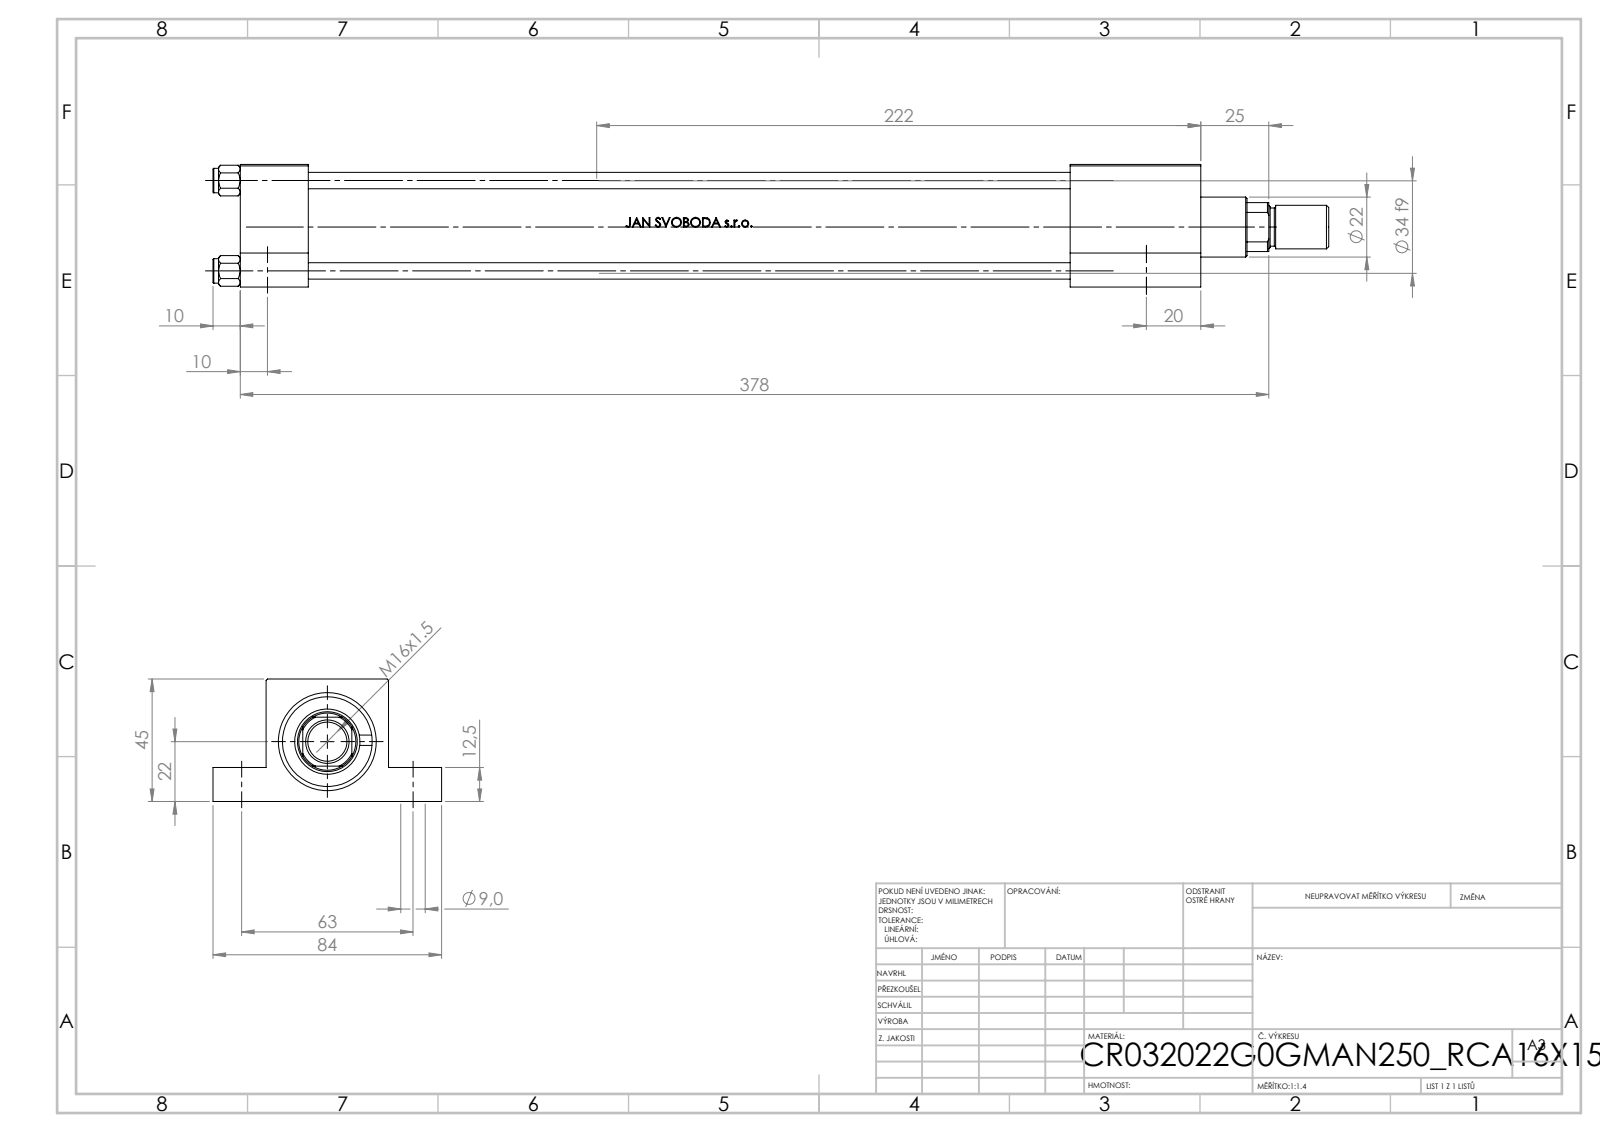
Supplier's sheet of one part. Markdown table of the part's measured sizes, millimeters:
| quantity | value |
| --- | --- |
| part name | V215CR_G_TYCINKA; V215_VC_A; ROD_END_AH; V215CR_VCP_G (+2 more) |
| STEP written by | SolidWorks 2019 (CONFIG_CONTROL_DESIGN) |
| units | millimeters |
| bodies | 12 solids, 1100 faces (434 planar, 128 cylindrical, 538 other) |
| overall size | 410 × 84 × 45 |
| volume | 437 540 mm³ |
| surface area | 164 036 mm² |
| round holes (diameter × count) | 6 × 4, 9 × 4, 7 × 2, 13.16 × 2, 20 × 2, 10.5 × 1, 22 × 1, 24 × 1, 25 × 1, 32 × 1, 33 × 1 |
| round bosses / shafts (diameter × count) | 9 × 4, 38 × 1, 34 × 1, 16 × 1, 14 × 1 |
| partial cylindrical surfaces (radius × count) | 10.5 × 1 |
| main face-to-face distances | 45, 25, 12.5, 32.5, 353, 19.5, 64.5, 328, 305, 280 |
| hole center spacings | 33.2, 23.13, 23.83, 46.95, 63, 323, 329.09, 305.5 |
